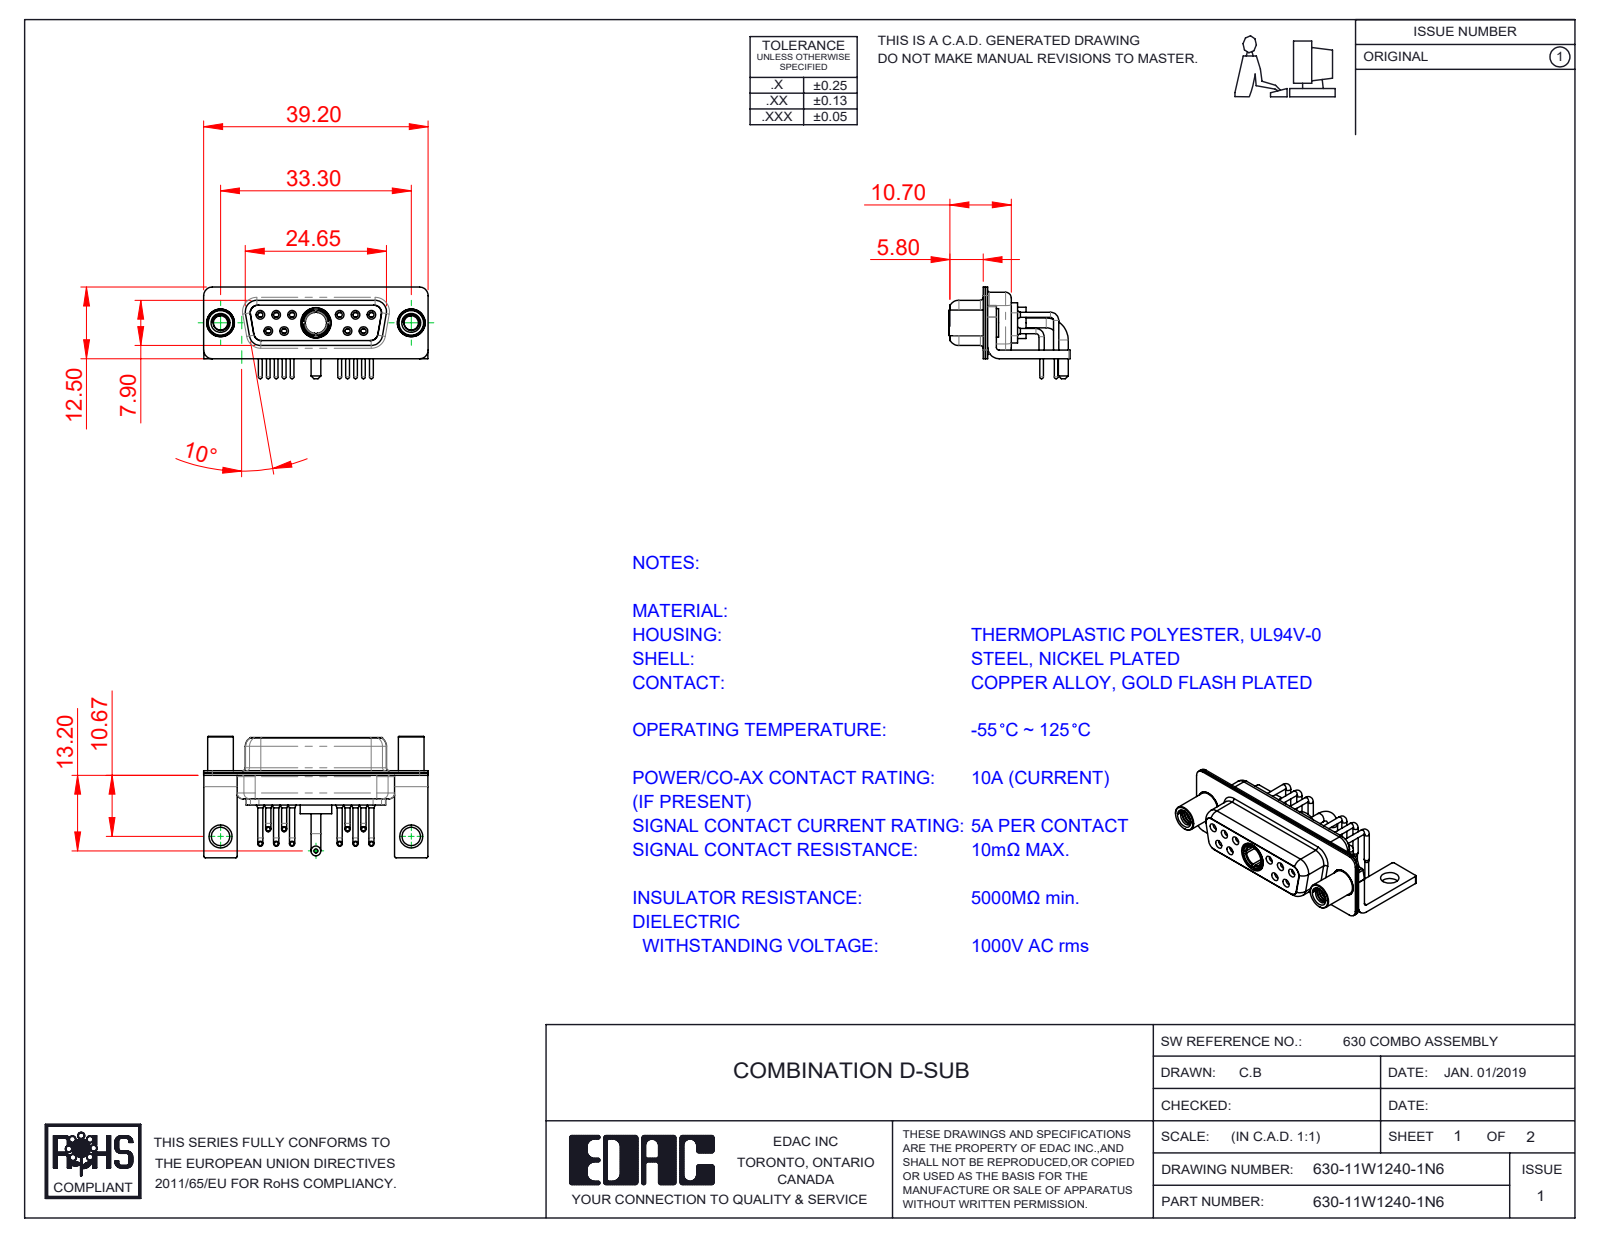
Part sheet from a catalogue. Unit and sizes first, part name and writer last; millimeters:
Units: millimetres
Overall size (bounding box): 39.2 × 21.2 × 16
Round holes (diameter × count): ⌀0.9 ×10, ⌀1.1 ×10, ⌀1.5 ×10, ⌀2 ×10, ⌀1.7 ×6, ⌀1.6 ×4, ⌀4.85 ×3, ⌀2.5 ×2, ⌀3.2 ×2, ⌀4 ×2, ⌀4.05 ×2, ⌀3.7 ×1
Round bosses / shafts (diameter × count): ⌀0.9 ×10, ⌀0.65 ×10, ⌀1.6 ×6, ⌀5 ×2, ⌀4.95 ×2, ⌀4.8 ×2, ⌀4.5 ×2, ⌀1.7 ×2
Partial cylindrical surfaces — rounded edges, fillets, slot ends (radius × count): R0.25 ×16, R1.5 ×16, R2 ×13, R1.35 ×12, R1.6 ×8, R0.5 ×5, R0.6 ×4, R0.65 ×4
Main face-to-face distances: 0.4, 0.8, 1.4, 0.45, 8.45, 1.5, 1.8, 8.9, 6.2, 2.3
Hole centre spacings: 3.16, 2.77, 13.85, 11.08, 16.62, 5.03, 5.04, 5.54
Volume: 2 972 mm³ · Surface area: 7 146 mm²
Bodies: 19 solids, 985 faces (268 planar, 464 cylindrical, 253 other)
Part name (STEP PRODUCT): 630Combo Housing_11W1; 630Combo Contact Row 2; 630Combo Contact Row 1; 630Combo Threaded Standoff_D (+5 more)
STEP written by: SolidWorks 2020 (CONFIG_CONTROL_DESIGN)
